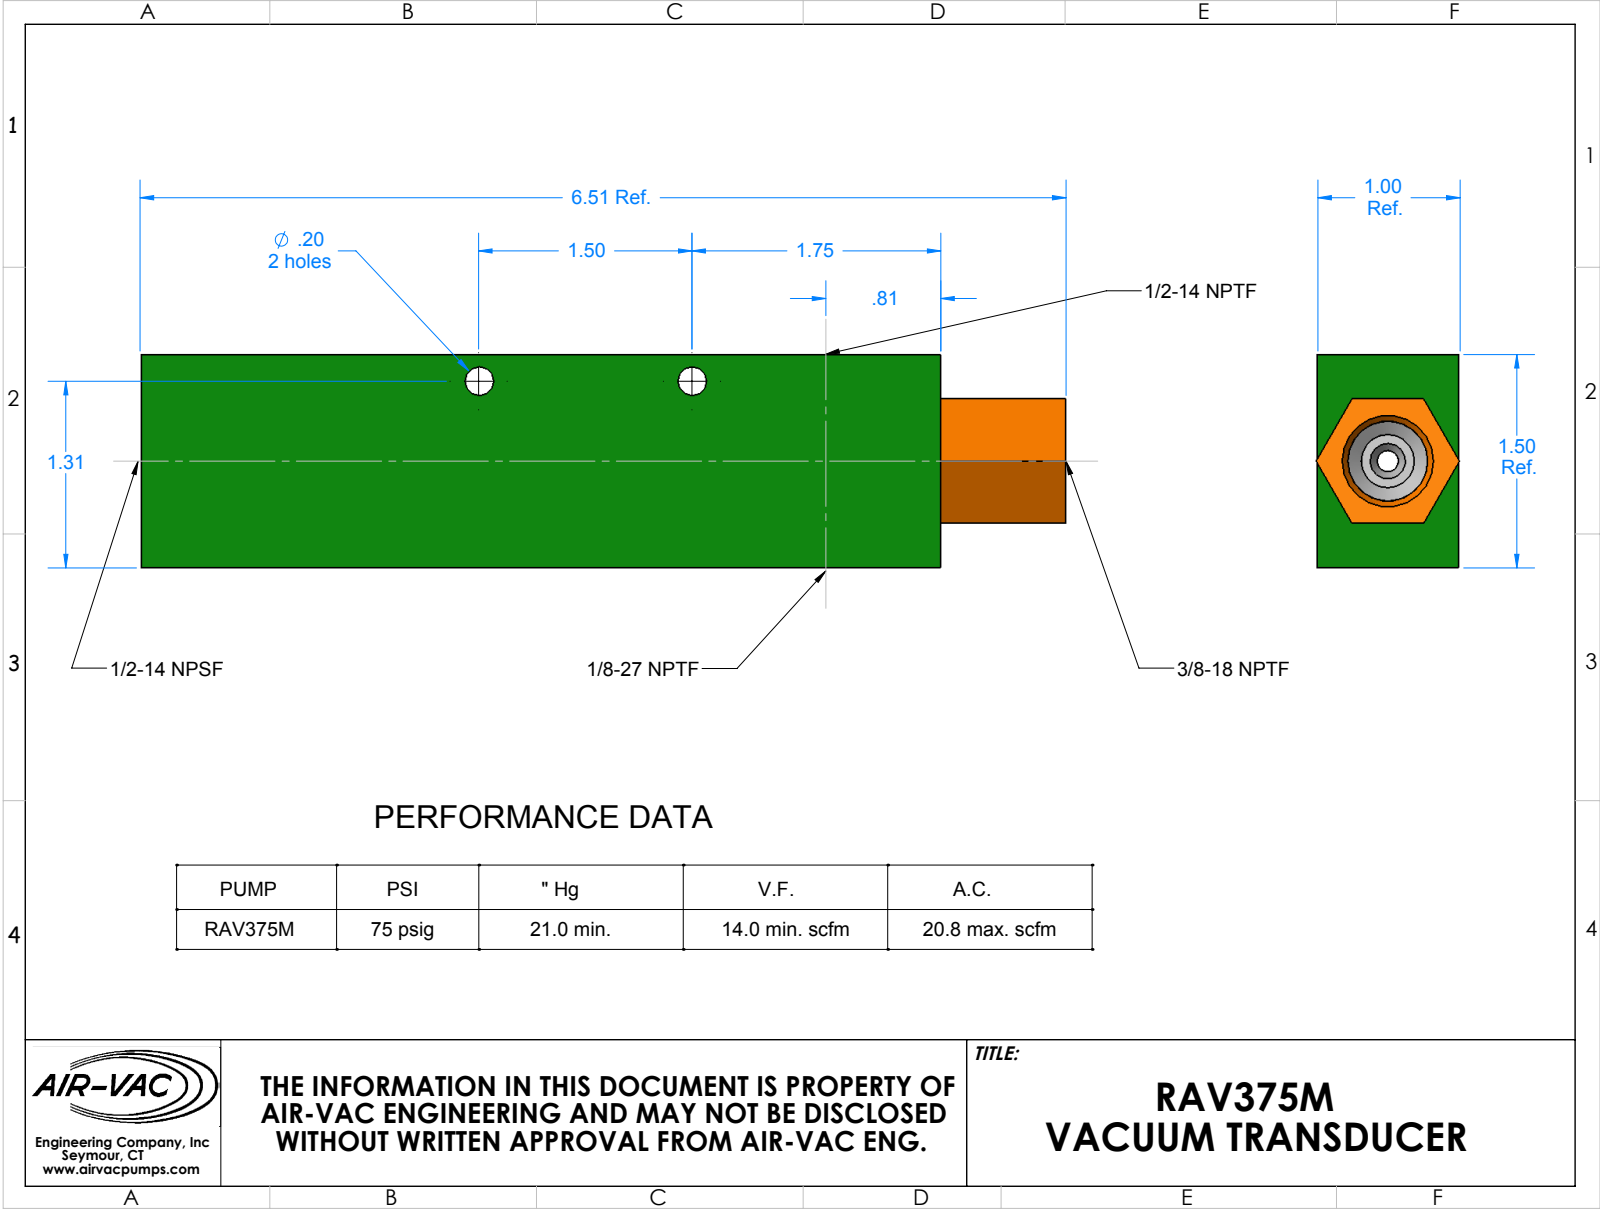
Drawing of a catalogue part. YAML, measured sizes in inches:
part_name: "RAV375M; TC3-37-3; RAV375B_Web Model; RAV375MG_Web Model (+1 more)"
step_written_by: "SolidWorks 2008 (AUTOMOTIVE_DESIGN)"
units: inches
bodies: {solids: 3, faces: 67, planar: 28, cylindrical: 19, other: 20}
overall_size: [6.51, 1.5, 1.01]
volume: 7.799
surface_area: 47.18
round_holes:
  - {diameter: 0.203, count: 2}
  - {diameter: 0.339, count: 1}
  - {diameter: 0.374, count: 1}
  - {diameter: 0.374, count: 1}
  - {diameter: 0.563, count: 1}
  - {diameter: 0.578, count: 1}
  - {diameter: 0.703, count: 1}
round_bosses_or_shafts:
  - {diameter: 0.532, count: 1}
face_to_face_distances: [1, 1.5, 5.63, 1.187, 0.313, 0.875, 0.875, 0.88, 6.51, 1.25]
hole_center_spacings: [1.5]
